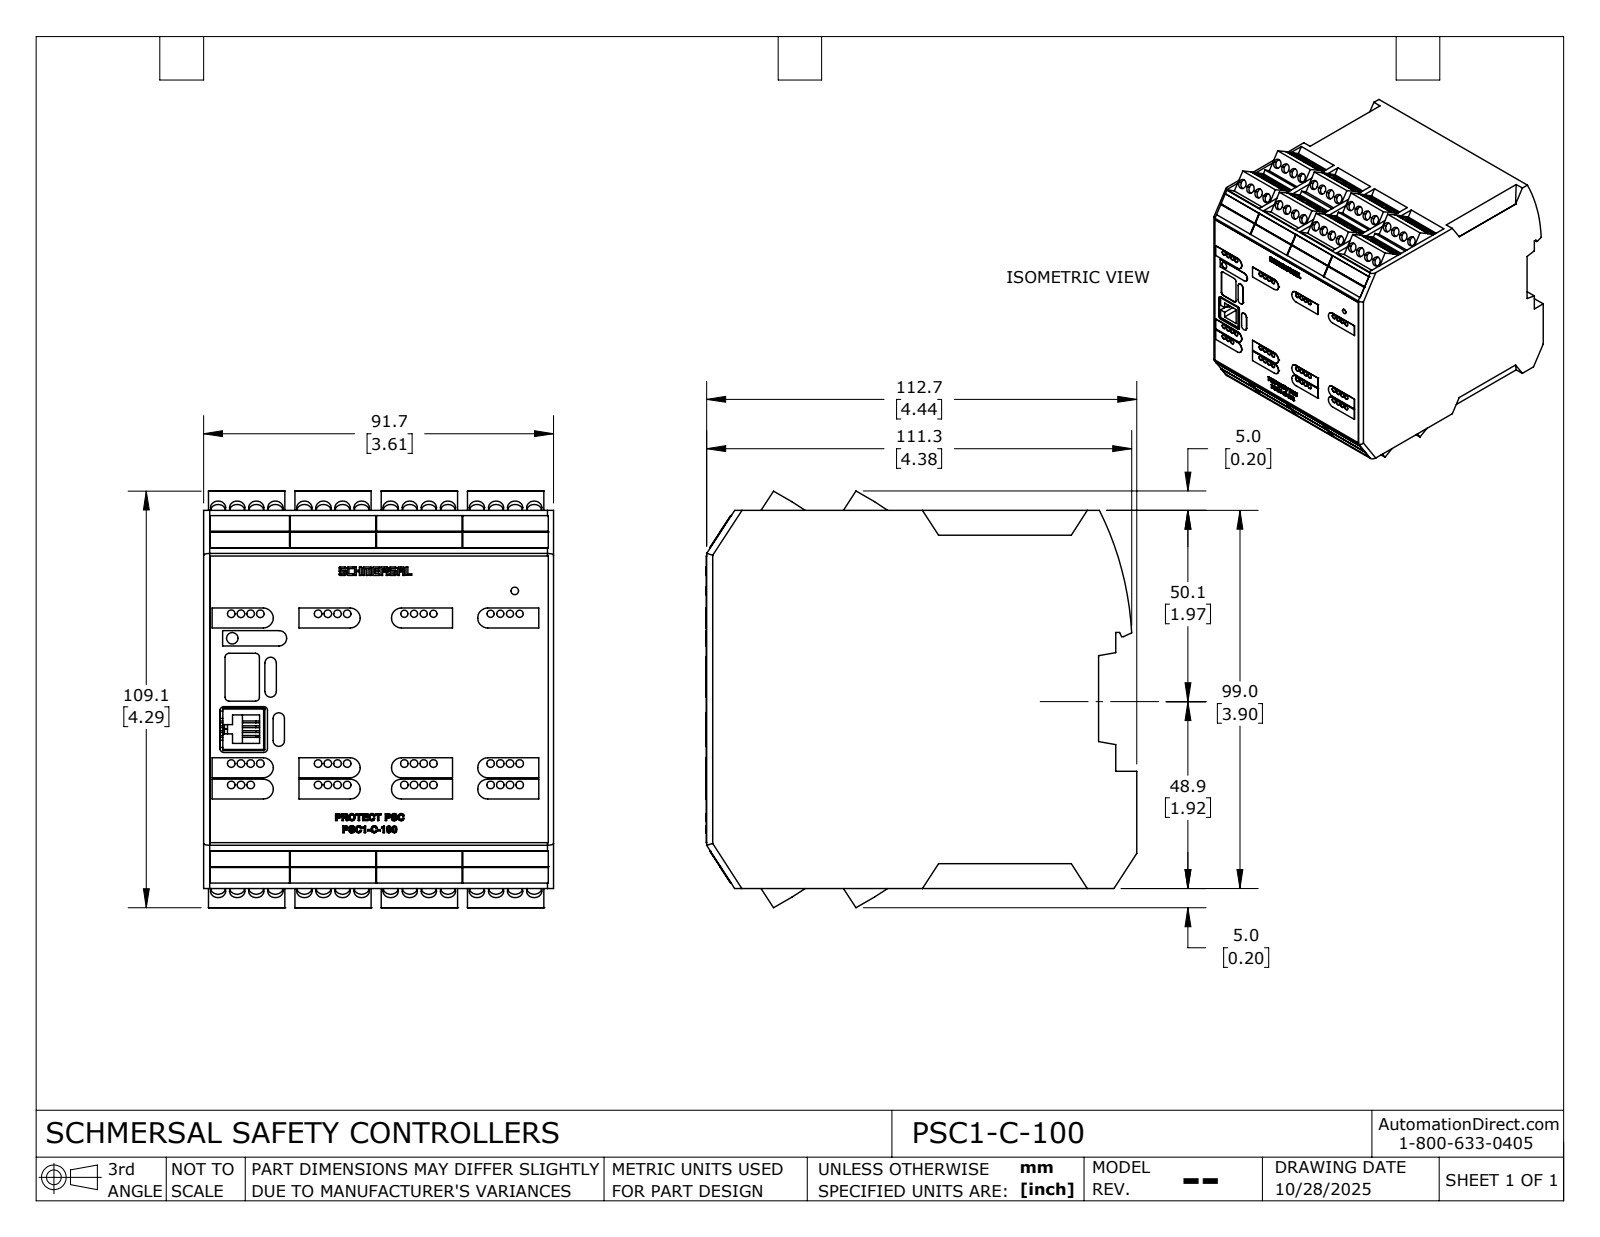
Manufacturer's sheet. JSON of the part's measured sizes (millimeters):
{"part_name": "PSC1-C-100", "step_written_by": "SolidWorks 2024 (AUTOMOTIVE_DESIGN)", "units": "millimeters", "bodies": {"solids": 1, "faces": 1693, "planar": 1002, "cylindrical": 335, "other": 356}, "overall_size": [112.85, 109.09, 91.65], "volume_mm3": 968677, "surface_area_mm2": 76075, "round_holes": [[4, 64], [2, 39], [1.89, 8], [3, 1]], "round_bosses_or_shafts": [[2, 1]], "partial_cylinders_radius": [[2.6, 12], [1, 10], [0.3, 8], [1.5, 6], [1.6, 6], [0.7, 4], [0.2, 2], [0.5, 2]], "face_to_face_distances": [91.65, 22.6, 45.2, 99, 20.05, 22.55, 2.55, 22.65, 42.65, 67.8], "hole_center_spacings": [22.6, 5, 12.78, 25.48, 17.6, 21.17, 27.6, 30]}
